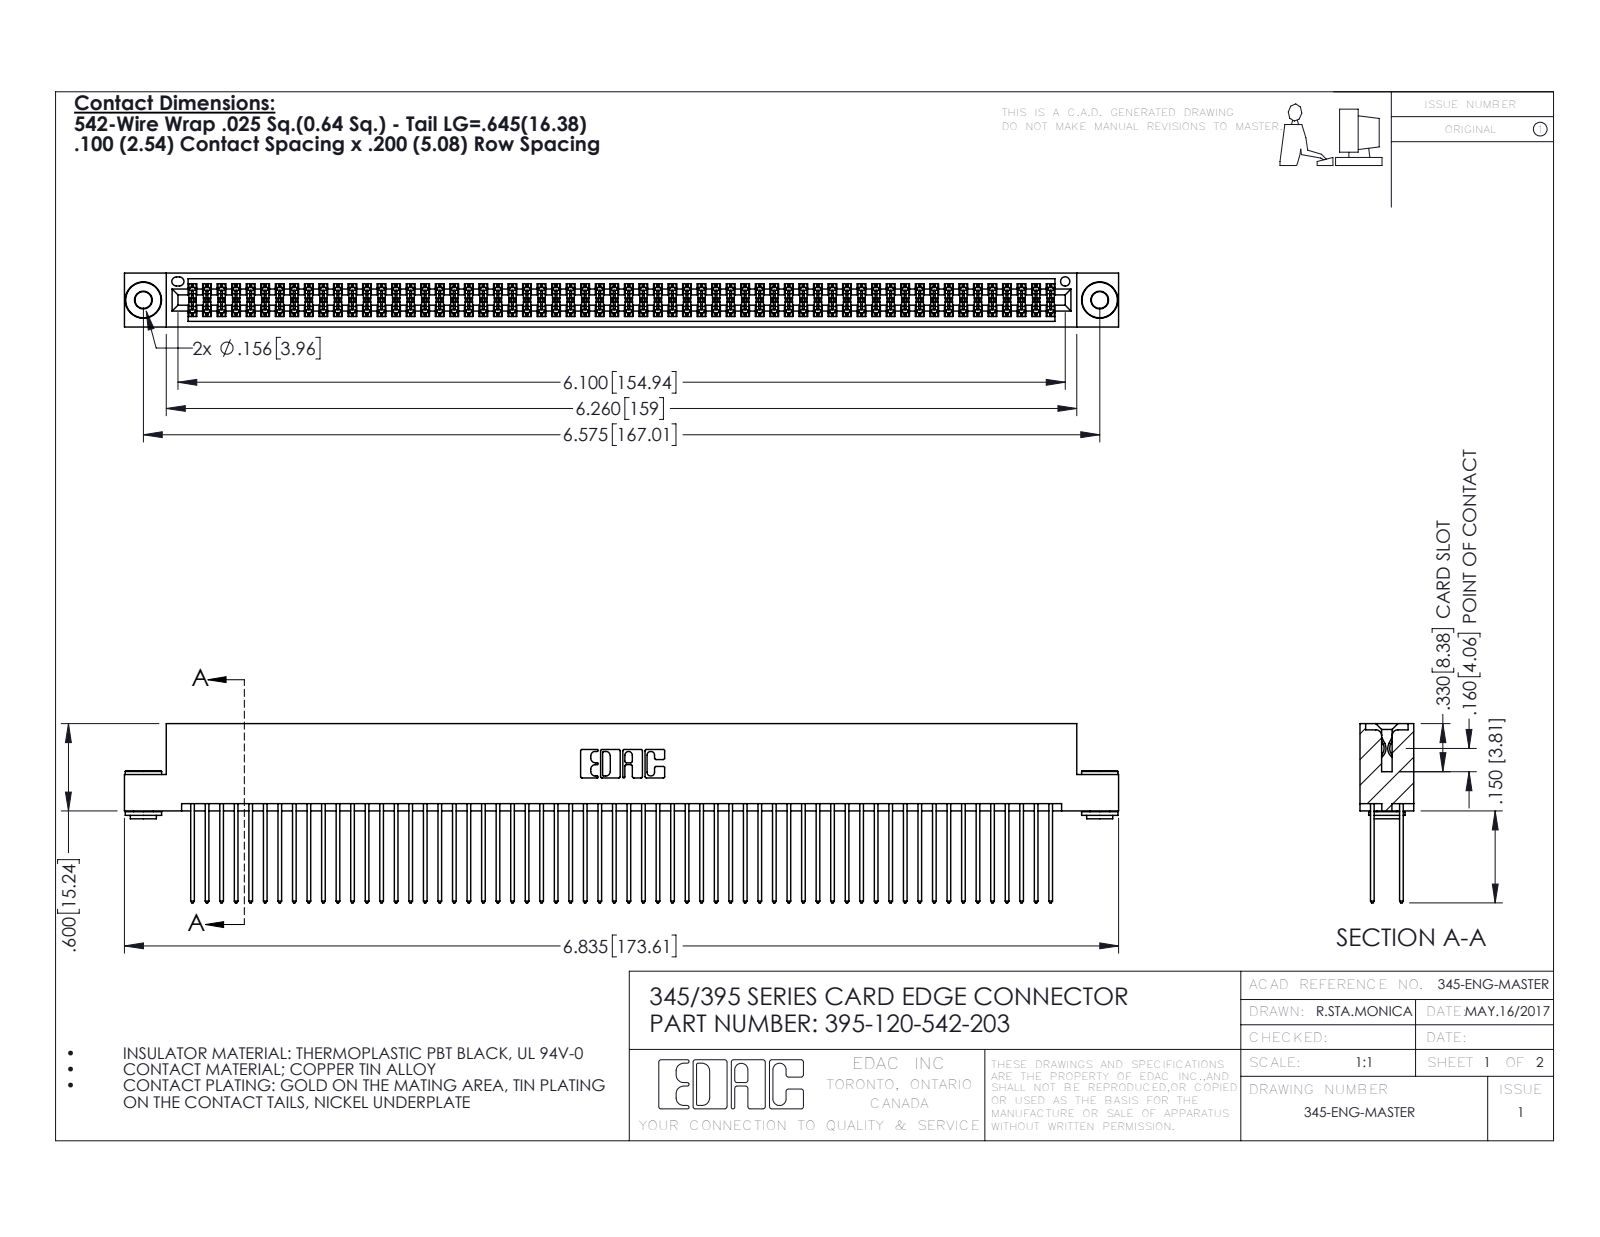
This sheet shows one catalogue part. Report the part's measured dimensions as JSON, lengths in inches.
{"part_name": "395-120-542-203; 345-250-002_345-250-002-102; 345-292-001_345-293-142; 345 Part_Flush Mounting Lugs - 0.156 Dia-TH", "step_written_by": "SolidWorks 2016 (CONFIG_CONTROL_DESIGN)", "units": "inches", "bodies": {"solids": 123, "faces": 6164, "planar": 4050, "cylindrical": 2106, "other": 8}, "overall_size": [6.835, 1.232, 0.37], "volume_in3": 1.075, "surface_area_in2": 45.26, "round_holes": [[0.116, 2], [0.156, 2], [0.064, 1]], "round_bosses_or_shafts": [[0.25, 2], [0.18, 2], [0.136, 2]], "partial_cylinders_radius": [[0.006, 180], [0.01, 120], [0.01, 22], [0.007, 6], [0.031, 6], [0.026, 3], [0.014, 2], [0.019, 2]], "face_to_face_distances": [0.072, 0.298, 0.2, 0.025, 0.098, 0.272, 0.225, 0.37, 0.175, 0.149], "hole_center_spacings": [0.27, 6.339, 6.575]}
